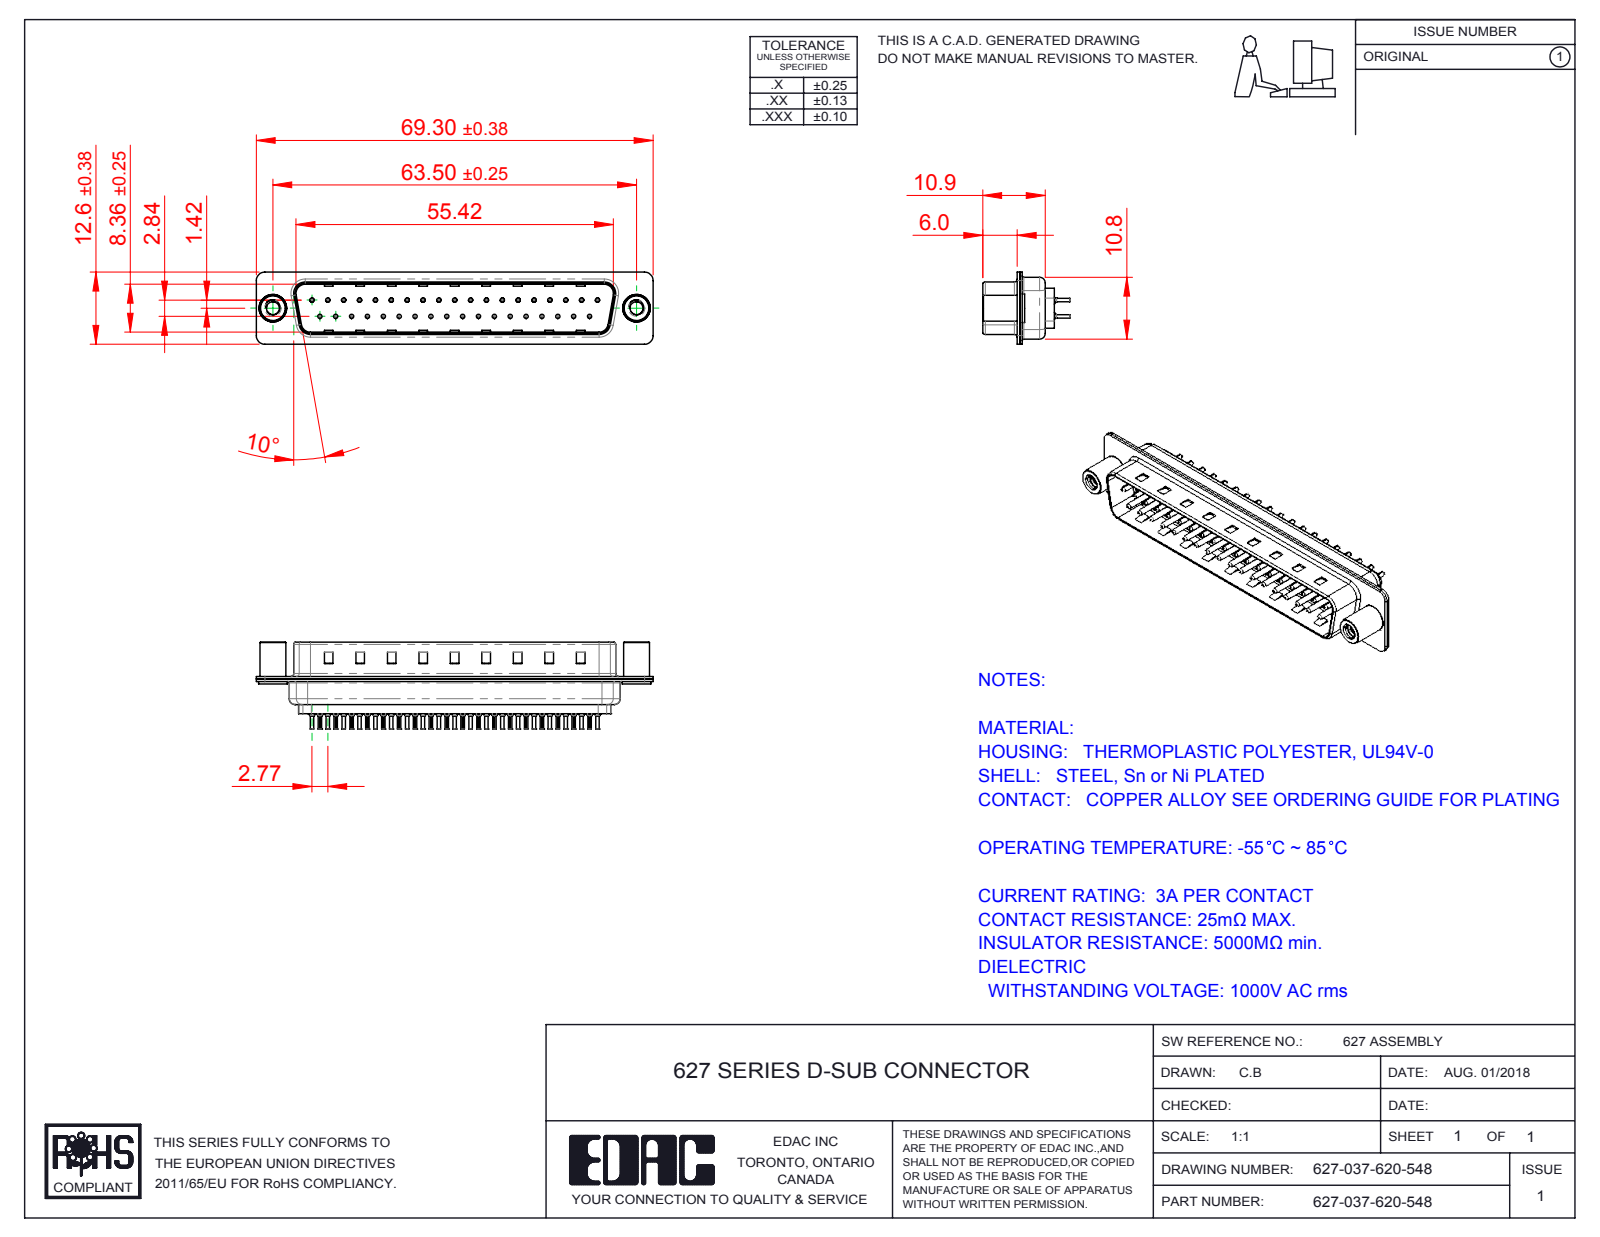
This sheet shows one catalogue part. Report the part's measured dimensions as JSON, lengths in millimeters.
{"part_name": "627-037-620-548; 627 Housing_37 LP; 627 4-40 Threaded Standoff; 627 Contact Row 1_20L (+3 more)", "step_written_by": "SolidWorks 2016 (CONFIG_CONTROL_DESIGN)", "units": "millimeters", "bodies": {"solids": 42, "faces": 4072, "planar": 1093, "cylindrical": 1538, "other": 1441}, "overall_size": [69.3, 15.2, 12.6], "volume_mm3": 3746, "surface_area_mm2": 10657, "round_holes": [[0.2, 37], [0.35, 37], [1.1, 37], [1.6, 37], [2.26, 2], [4, 2], [4.8, 2]], "round_bosses_or_shafts": [[2, 37], [1.5, 37], [0.75, 37], [0.6, 37], [5, 2], [4.9, 2], [4.5, 2]], "partial_cylinders_radius": [[0.1, 74], [1.5, 16], [2, 12], [0.5, 8], [1.6, 8], [0.25, 4], [0.6, 4], [0.65, 4]], "face_to_face_distances": [0.4, 0.82, 9.58, 0.45, 8.76, 1.5, 0.9, 1.4, 6.05, 0.42], "hole_center_spacings": [3.16, 2.77, 5.54, 8.31, 5.04, 10.1, 11.08, 12.78]}
